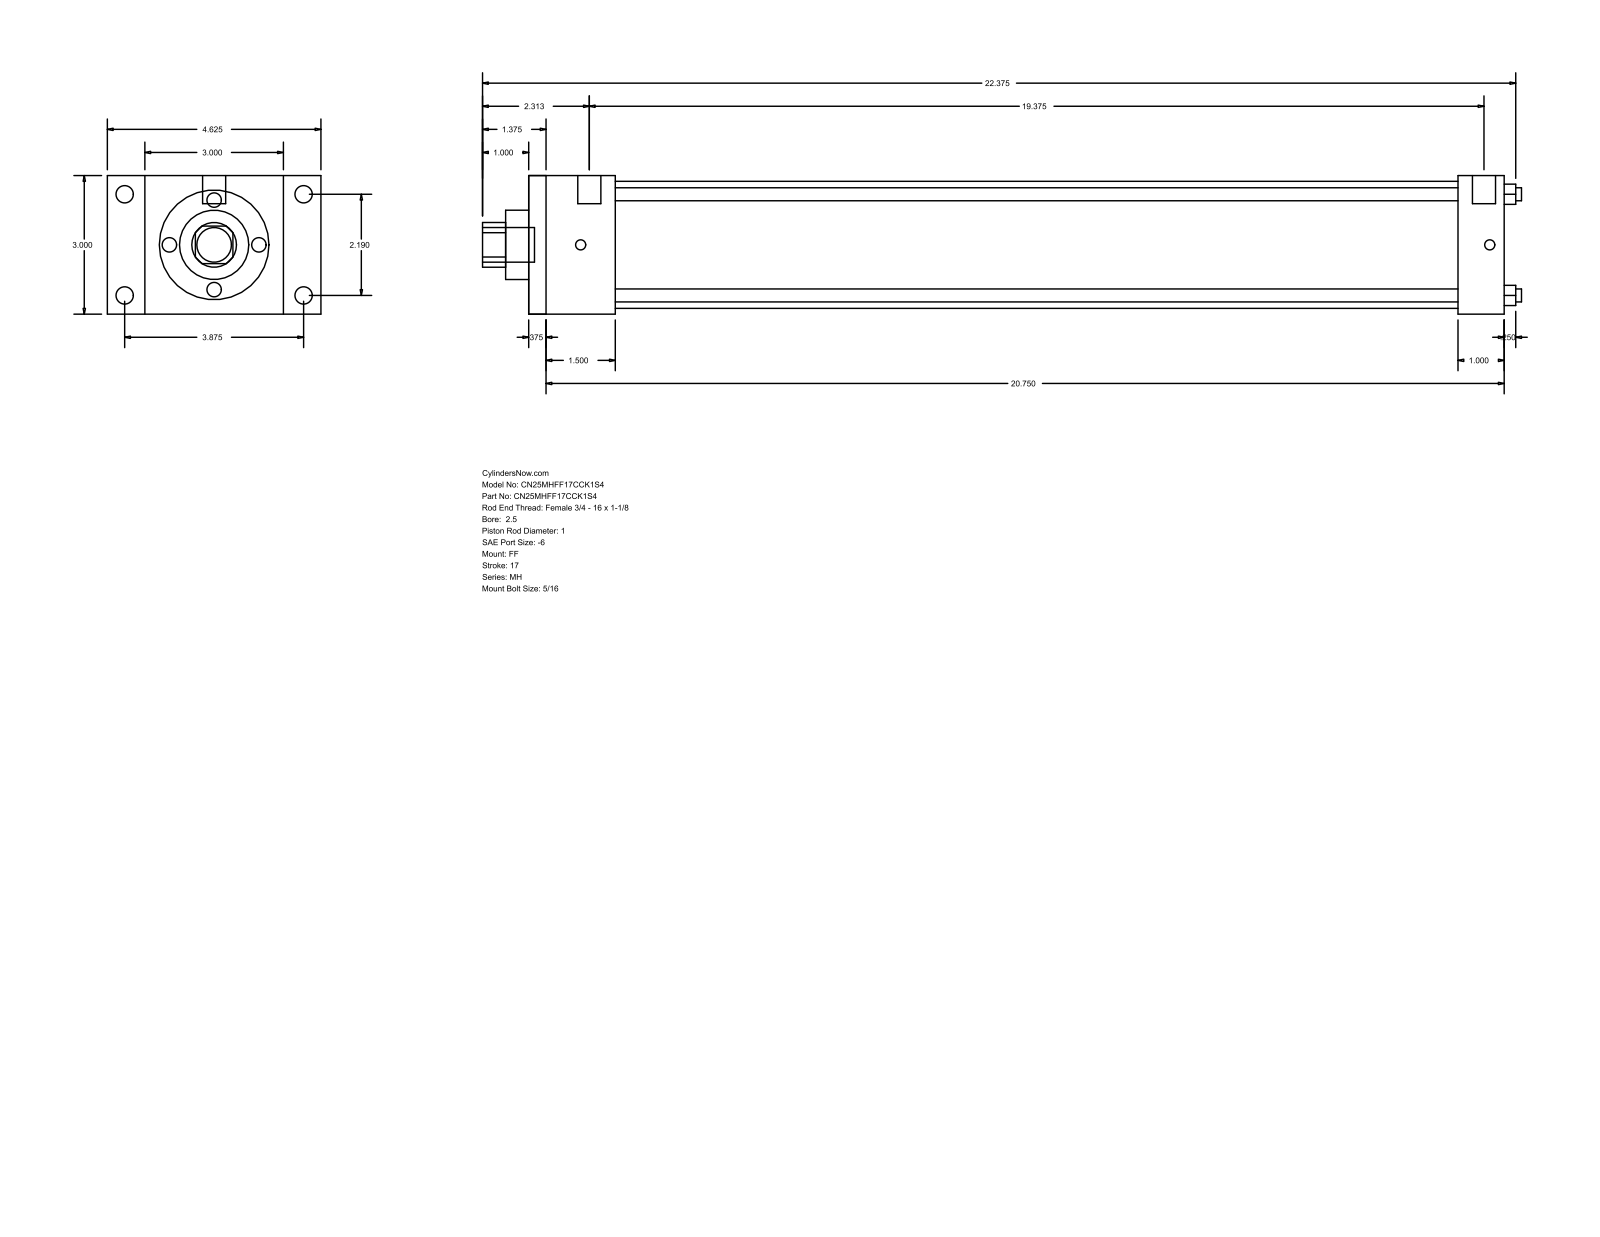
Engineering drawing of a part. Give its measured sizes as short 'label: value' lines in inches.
name: MH_FF__0250_1
written by: GSSL Pune (CONFIG_CONTROL_DESIGN)
unit: in
bodies: 0 solids, 92 faces (64 planar, 28 cylindrical, 0 other)
size: 22.5 × 4.625 × 3
holes: 4× ⌀0.281, 1× ⌀1, 1× ⌀1.5, 1× ⌀2.75
bosses: 4× ⌀0.375, 4× ⌀0.219, 2× ⌀0.5, 1× ⌀0.75
rounds: 1× R0.484
face distances: 3, 21.125, 0.375, 20.75, 1, 1.875, 20.125, 1.5, 19.75, 18.25
hole spacings: 1.548, 2.19, 3.097
